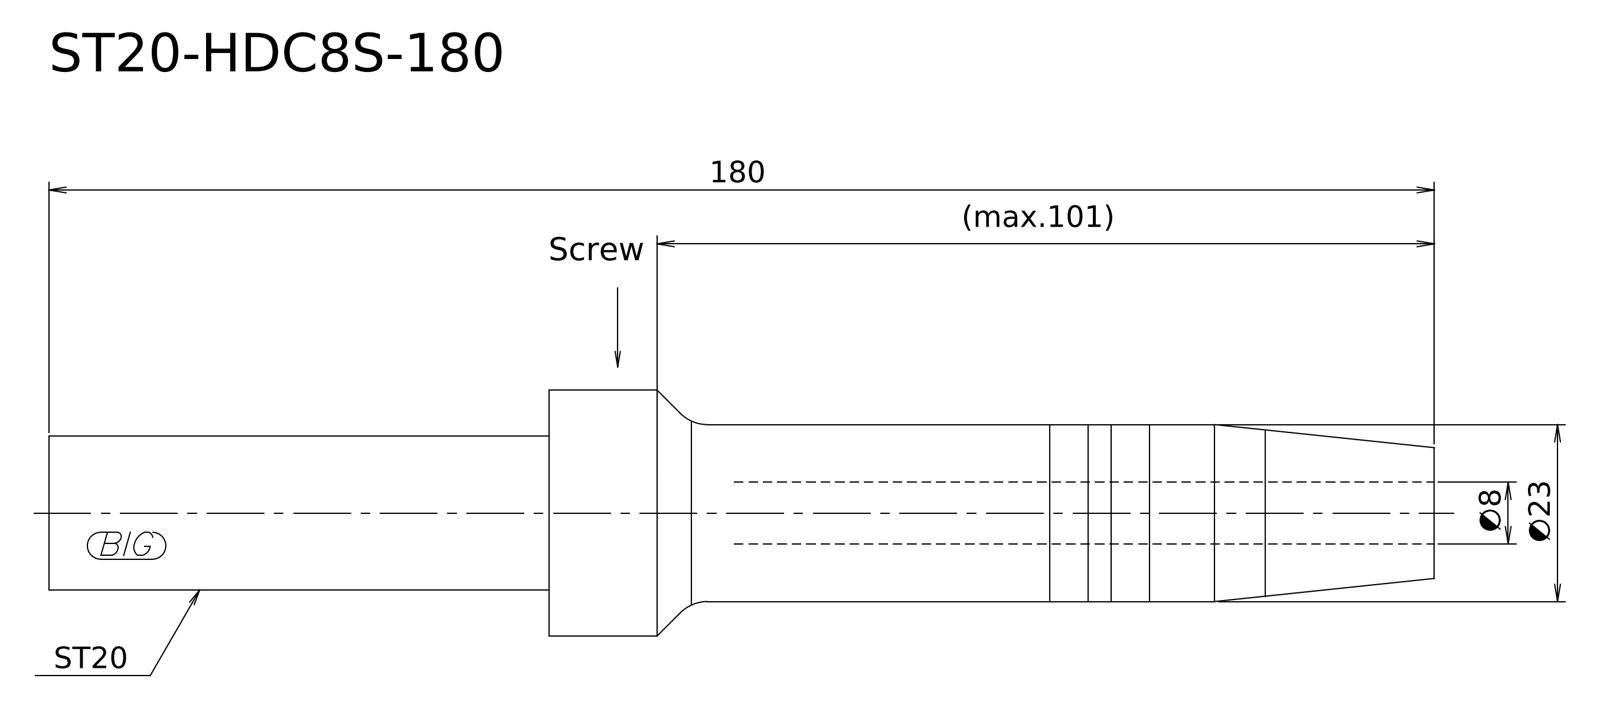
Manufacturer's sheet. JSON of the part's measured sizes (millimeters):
{"step_written_by": "Kubotek KeyCreator V8.5.1 (14335) (CONFIG_CONTROL_DESIGN)", "units": "millimeters", "bodies": {"solids": 1, "faces": 9, "planar": 3, "cylindrical": 3, "other": 3}, "overall_size": [180, 32, 32], "volume_mm3": 71759, "surface_area_mm2": 13771, "round_bosses_or_shafts": [[32, 1], [23, 1], [20, 1]], "face_to_face_distances": [65, 115, 180]}
